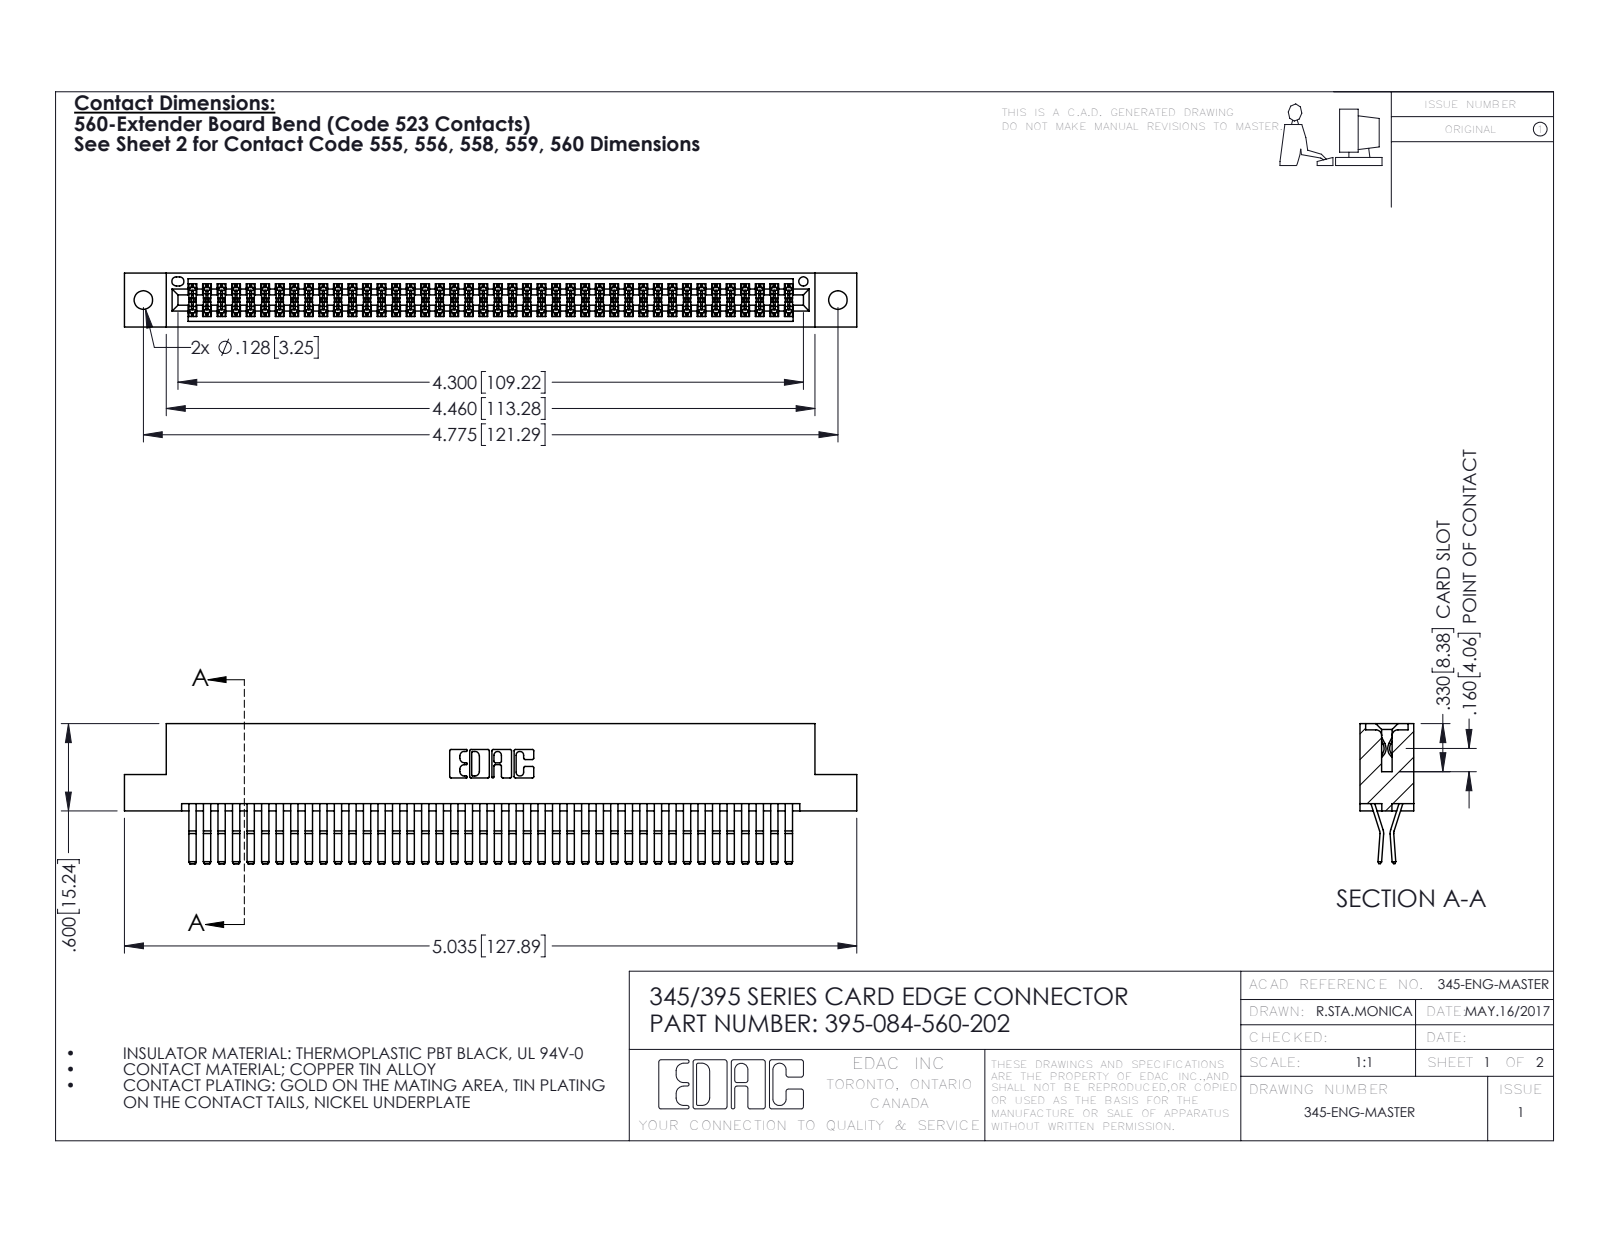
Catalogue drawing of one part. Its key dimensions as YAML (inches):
part_name: "345-292-001_560 Tail; 395-084-560-202; 345 Part_Flush Mounting Lugs - 0.128 Dia"
step_written_by: "SolidWorks 2016 (CONFIG_CONTROL_DESIGN)"
units: inches
bodies: {solids: 85, faces: 4494, planar: 2852, cylindrical: 1642, other: 0}
overall_size: [5.035, 0.962, 0.37]
volume: 0.789
surface_area: 31.41
round_holes:
  - {diameter: 0.128, count: 2}
  - {diameter: 0.064, count: 1}
partial_cylinders:
  - {radius: 0.006, count: 126}
  - {radius: 0.01, count: 22}
  - {radius: 0.007, count: 6}
  - {radius: 0.031, count: 6}
  - {radius: 0.026, count: 3}
  - {radius: 0.01, count: 2}
  - {radius: 0.014, count: 2}
  - {radius: 0.019, count: 2}
face_to_face_distances: [0.025, 0.298, 0.072, 0.2, 0.37, 0.098, 0.272, 0.225, 0.175, 0.149]
hole_center_spacings: [0.27, 4.539, 4.775]
